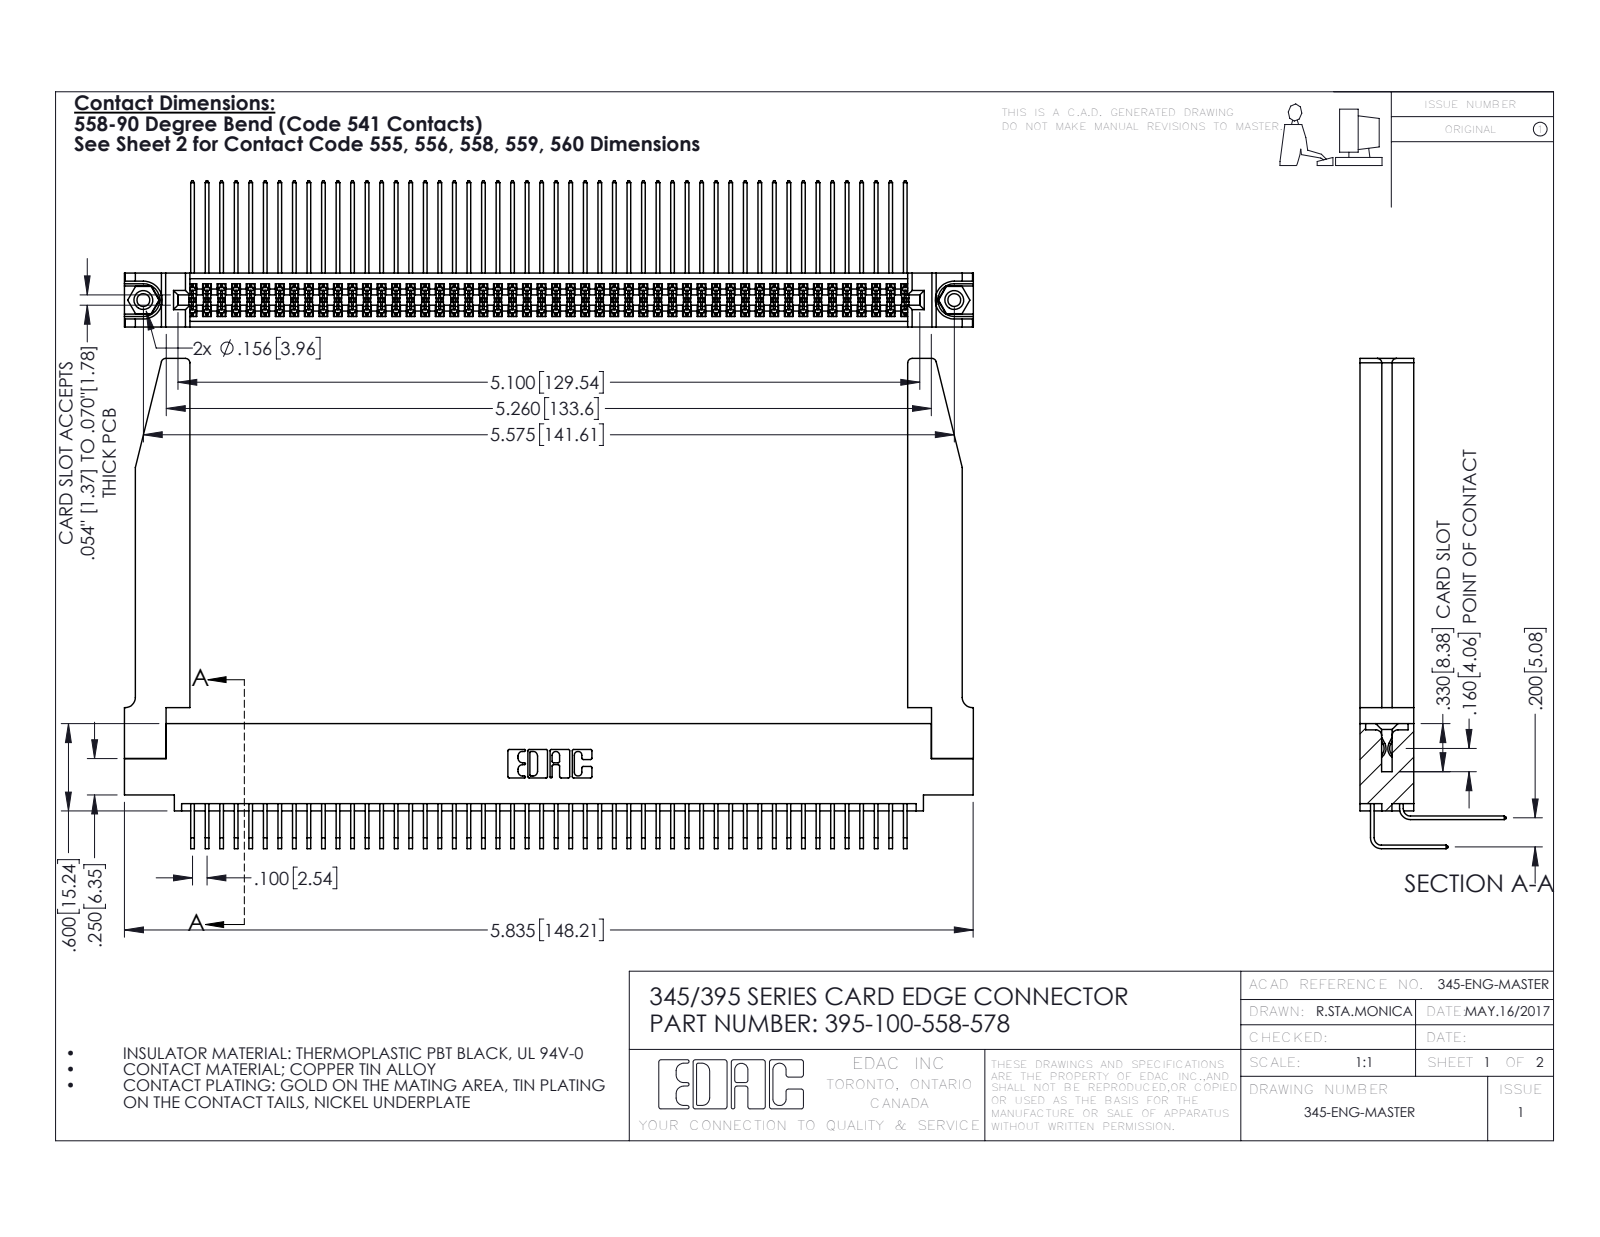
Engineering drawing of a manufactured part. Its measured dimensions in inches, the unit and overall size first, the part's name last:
Units: inches
Overall size (bounding box): 5.836 × 3.369 × 1.005
Round holes (diameter × count): ⌀0.089 ×2, ⌀0.125 ×2, ⌀0.156 ×2, ⌀0.064 ×1
Round bosses / shafts (diameter × count): ⌀0.155 ×2
Partial cylindrical surfaces — rounded edges, fillets, slot ends (radius × count): R0.006 ×151, R0.01 ×22, R0.03 ×8, R0.007 ×6, R0.031 ×6, R0.026 ×3, R0.014 ×2, R0.019 ×2
Main face-to-face distances: 0.072, 0.298, 0.37, 0.2, 0.098, 0.272, 0.025, 0.225, 0.025, 0.175
Hole centre spacings: 0.27, 5.339, 5.575
Volume: 1.388 in³ · Surface area: 49.5 in²
Bodies: 105 solids, 5564 faces (3726 planar, 1786 cylindrical, 52 other)
Part name (STEP PRODUCT): 345-250-001_345-250-001-102; 345-292-001_558 Tail - 2; 345-220-078_345-220-078; 345 Part_0.110 Offset - 0.156 Dia-TH (+2 more)
STEP written by: SolidWorks 2016 (CONFIG_CONTROL_DESIGN)
